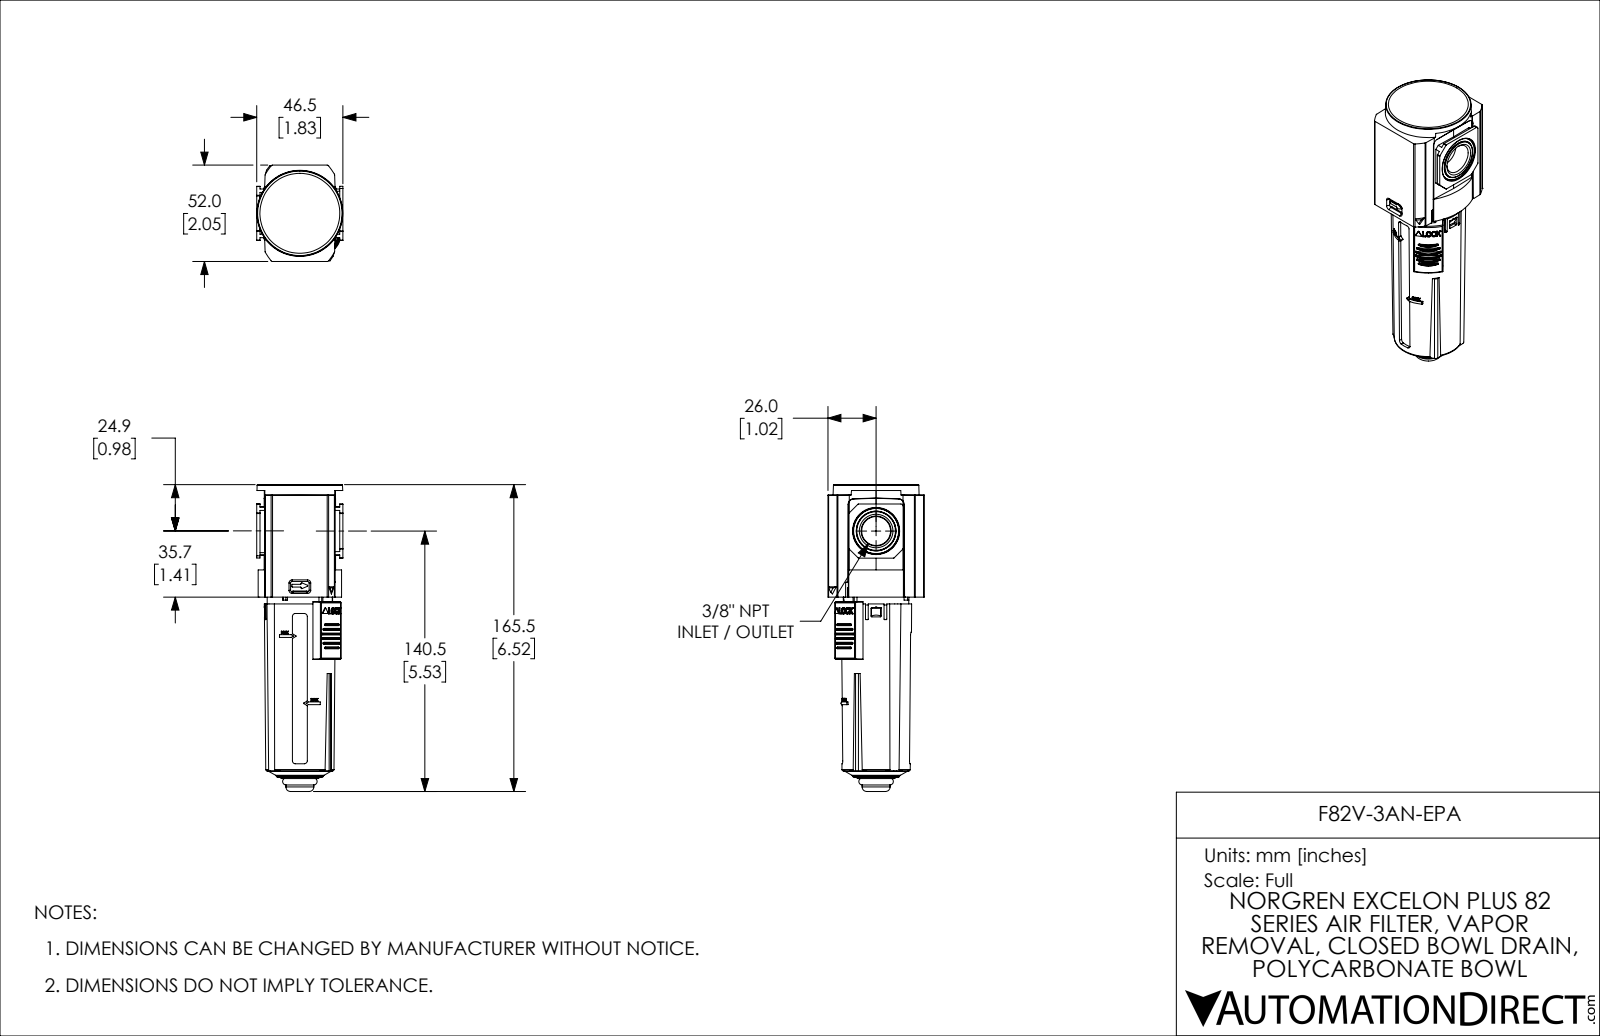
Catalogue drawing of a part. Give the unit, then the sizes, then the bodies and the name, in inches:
Units: inches
Overall size (bounding box): 6.515 × 2.047 × 1.831
Round holes (diameter × count): ⌀0.059 ×2, ⌀0.128 ×2, ⌀0.63 ×1
Round bosses / shafts (diameter × count): ⌀1.388 ×1, ⌀1.356 ×1, ⌀1.291 ×1, ⌀1.257 ×1, ⌀0.906 ×1, ⌀0.626 ×1, ⌀0.594 ×1
Partial cylindrical surfaces — rounded edges, fillets, slot ends (radius × count): R0.02 ×58, R0.039 ×30, R0.012 ×11, R0.008 ×10, R0.01 ×10, R0.031 ×8, R0.036 ×8, R0.048 ×8
Main face-to-face distances: 0.059, 1.988, 2.047, 1.929, 0.058, 2.093, 2.151, 0.182, 0.236, 1.352
Hole centre spacings: 0.797, 0.531, 0.594, 1.063, 1.189
Volume: 13.15 in³ · Surface area: 87.66 in²
Bodies: 5 solids, 1034 faces (457 planar, 381 cylindrical, 196 other)
Part name (STEP PRODUCT): F82V-3AN-EPA
STEP written by: SolidWorks 2021 (CONFIG_CONTROL_DESIGN)
